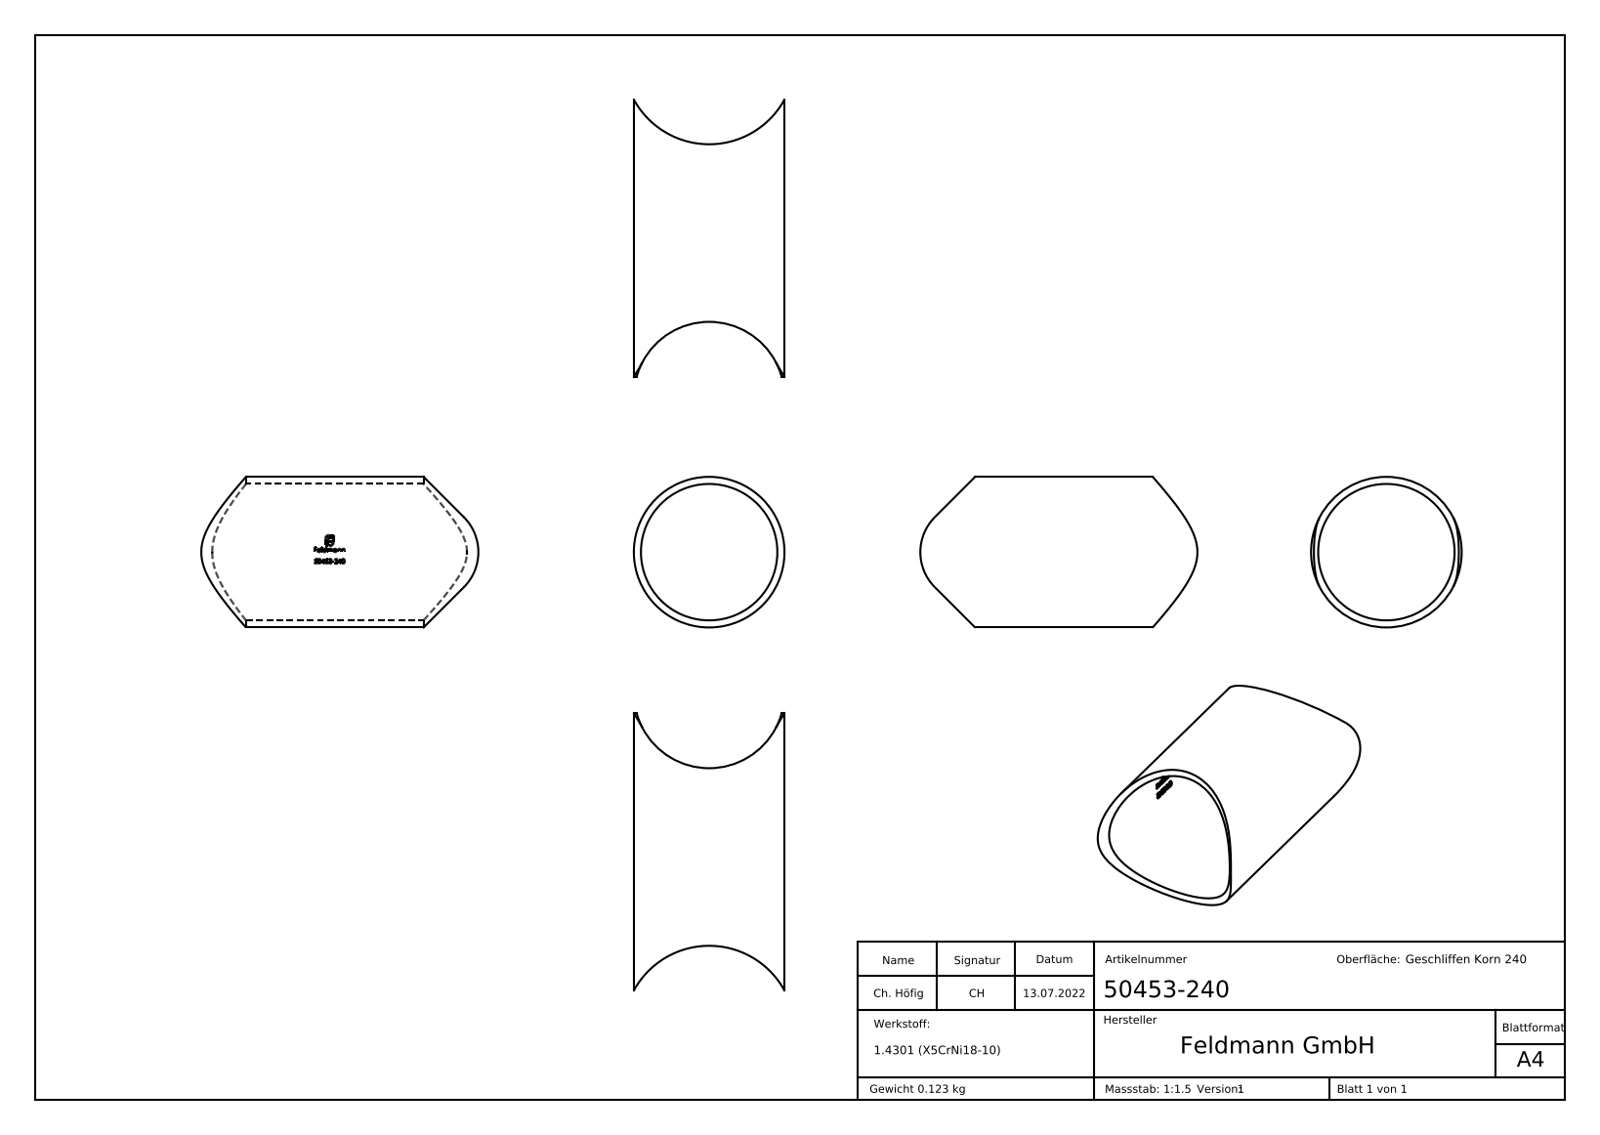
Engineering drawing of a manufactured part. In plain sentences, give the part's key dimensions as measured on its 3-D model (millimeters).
The part is named "50453-240". Its 3-D file was written by "SolidWorks 2018 (CONFIG_CONTROL_DESIGN)". It is 1 solid with 280 faces: 127 planar, 31 cylindrical and 122 other. Overall it measures 78 by 42.4 by 42.4 millimeters. Its volume is 15 610 cubic millimeters and its surface area 16 328 square millimeters. Round holes: 1 of diameter 38.4. Round bosses or shafts: 1 of diameter 42.4. Partial cylindrical surfaces (rounded edges, fillets, slot ends): 1 of radius 13.96, 1 of radius 19.3, 1 of radius 21.2, 1 of radius 24.15. The main face-to-face distances are 4.39, 1.82, 2.9, 0.88, 3.27, 0.92, 0.34, 2.74, 3.21, 7.75.
